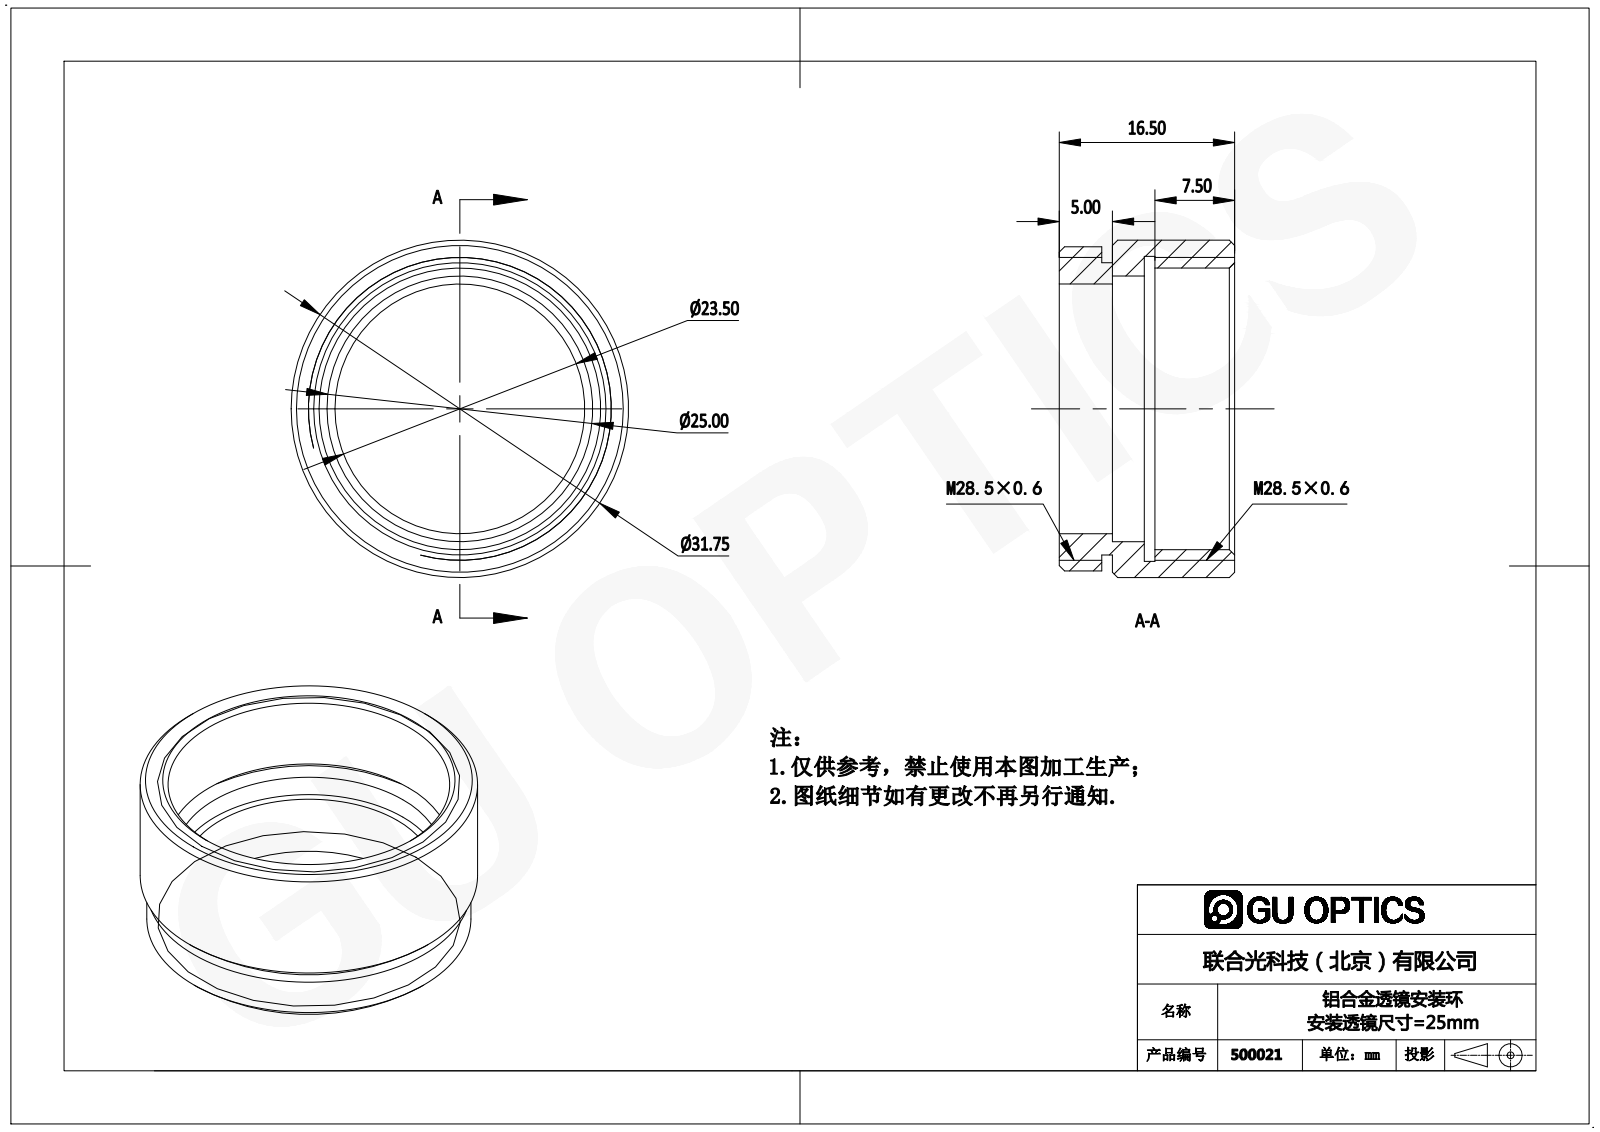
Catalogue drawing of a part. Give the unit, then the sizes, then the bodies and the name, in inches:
Units: inches
Overall size (bounding box): 1.25 × 1.25 × 0.65
Round holes (diameter × count): ⌀0.925 ×1, ⌀0.984 ×1, ⌀1.043 ×1, ⌀1.13 ×1
Round bosses / shafts (diameter × count): ⌀1.25 ×1, ⌀1.201 ×1, ⌀1.083 ×1
Main face-to-face distances: 0.157, 0.039, 0.118, 0.197, 0.276, 0.079, 0.65, 0.453, 0.374, 0.492
Volume: 0.25 in³ · Surface area: 6.214 in²
Bodies: 1 solid, 29 faces (7 planar, 14 cylindrical, 8 other)
Part name (STEP PRODUCT): 500021
STEP written by: SolidWorks 2016 (AUTOMOTIVE_DESIGN)
